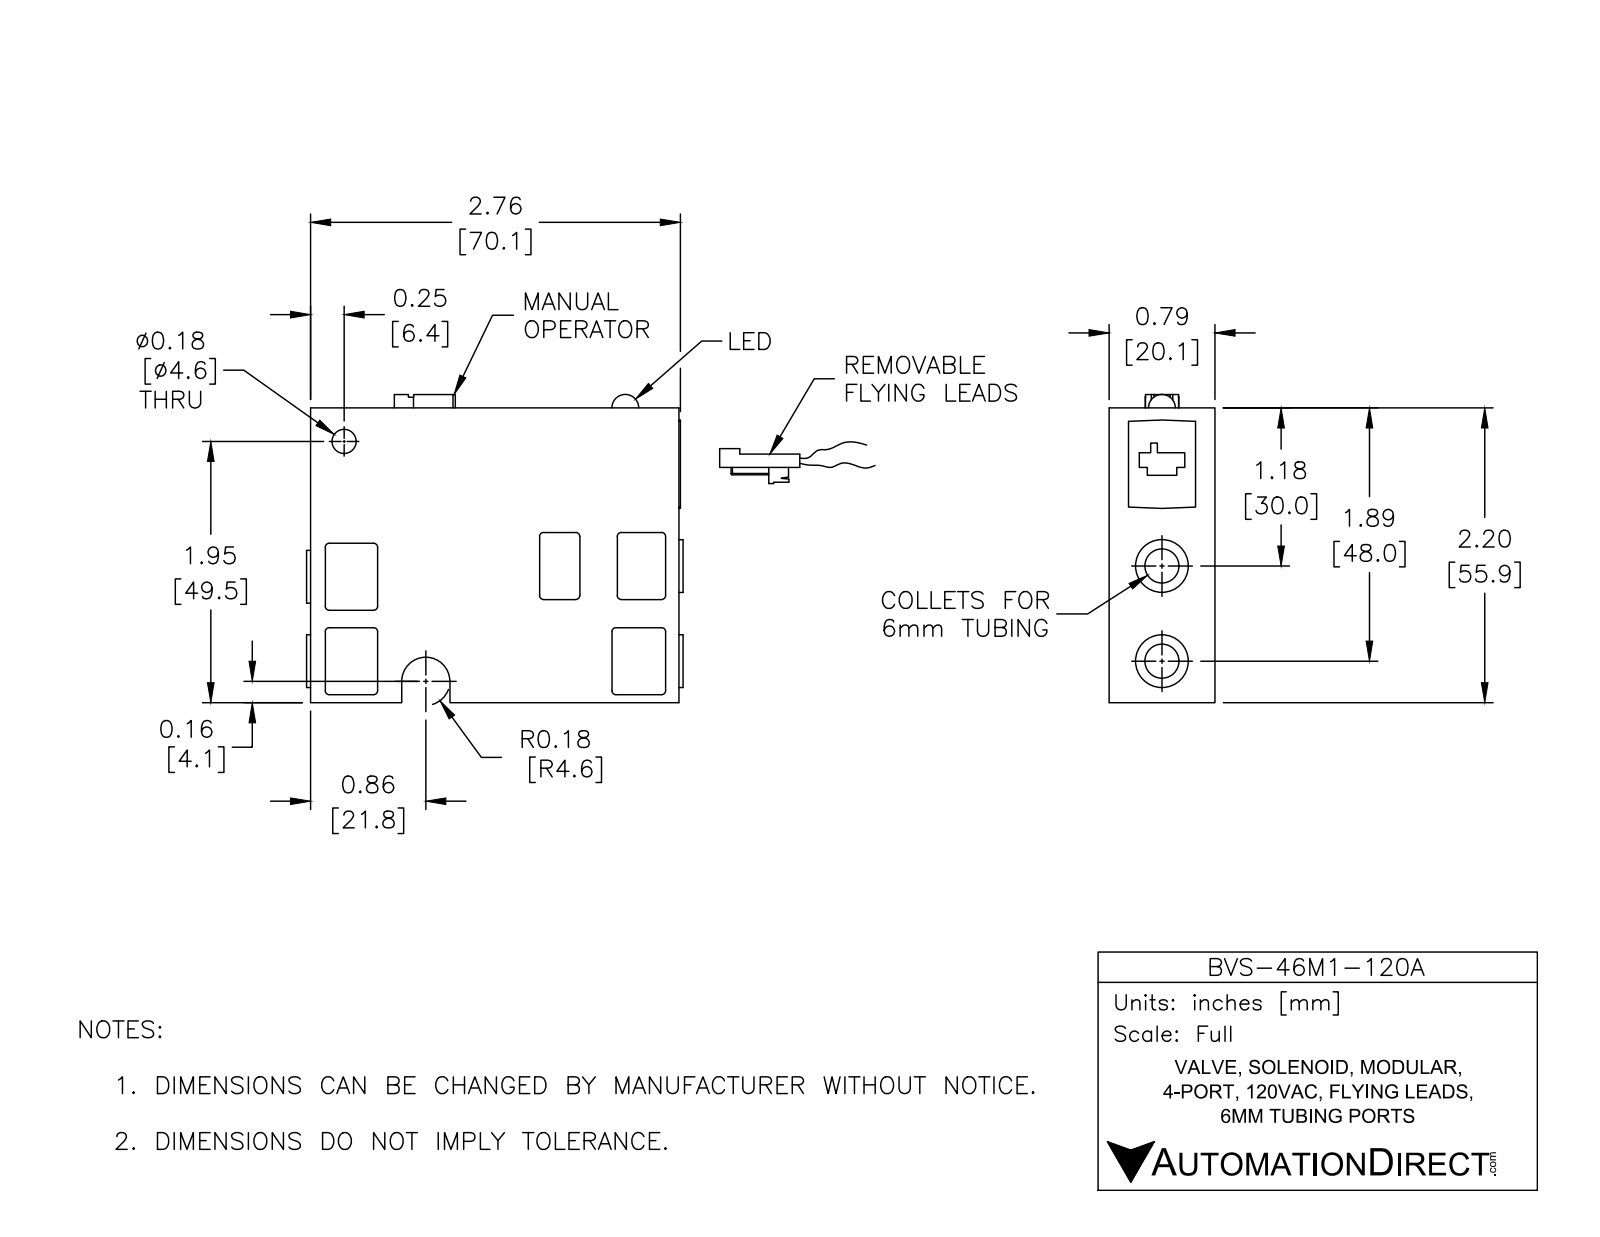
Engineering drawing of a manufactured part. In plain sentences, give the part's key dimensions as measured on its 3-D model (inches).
The part is named "BVS-46M1-120A". Its 3-D file was written by "SolidWorks 2016 (AUTOMOTIVE_DESIGN)". It is 1 solid with 173 faces: 85 planar, 78 cylindrical and 10 other. Overall it measures 3.009 by 2.3 by 0.79 inches. Its volume is 4.377 cubic inches and its surface area 25.04 square inches. Round holes: 3 of diameter 0.25, 1 of diameter 0.1, 1 of diameter 0.18. Round bosses or shafts: 6 of diameter 0.06, 3 of diameter 0.394. Partial cylindrical surfaces (rounded edges, fillets, slot ends): 20 of radius 0.03, 2 of radius 0.02, 1 of radius 0.125, 1 of radius 0.18. The main face-to-face distances are 0.79, 0.1, 2.2, 0.69, 2.75, 0.59, 0.5, 0.11, 2.65, 2.76. The hole center spacings are 0.08, 0.55, 0.63, 0.63, 0.71, 1.26.
